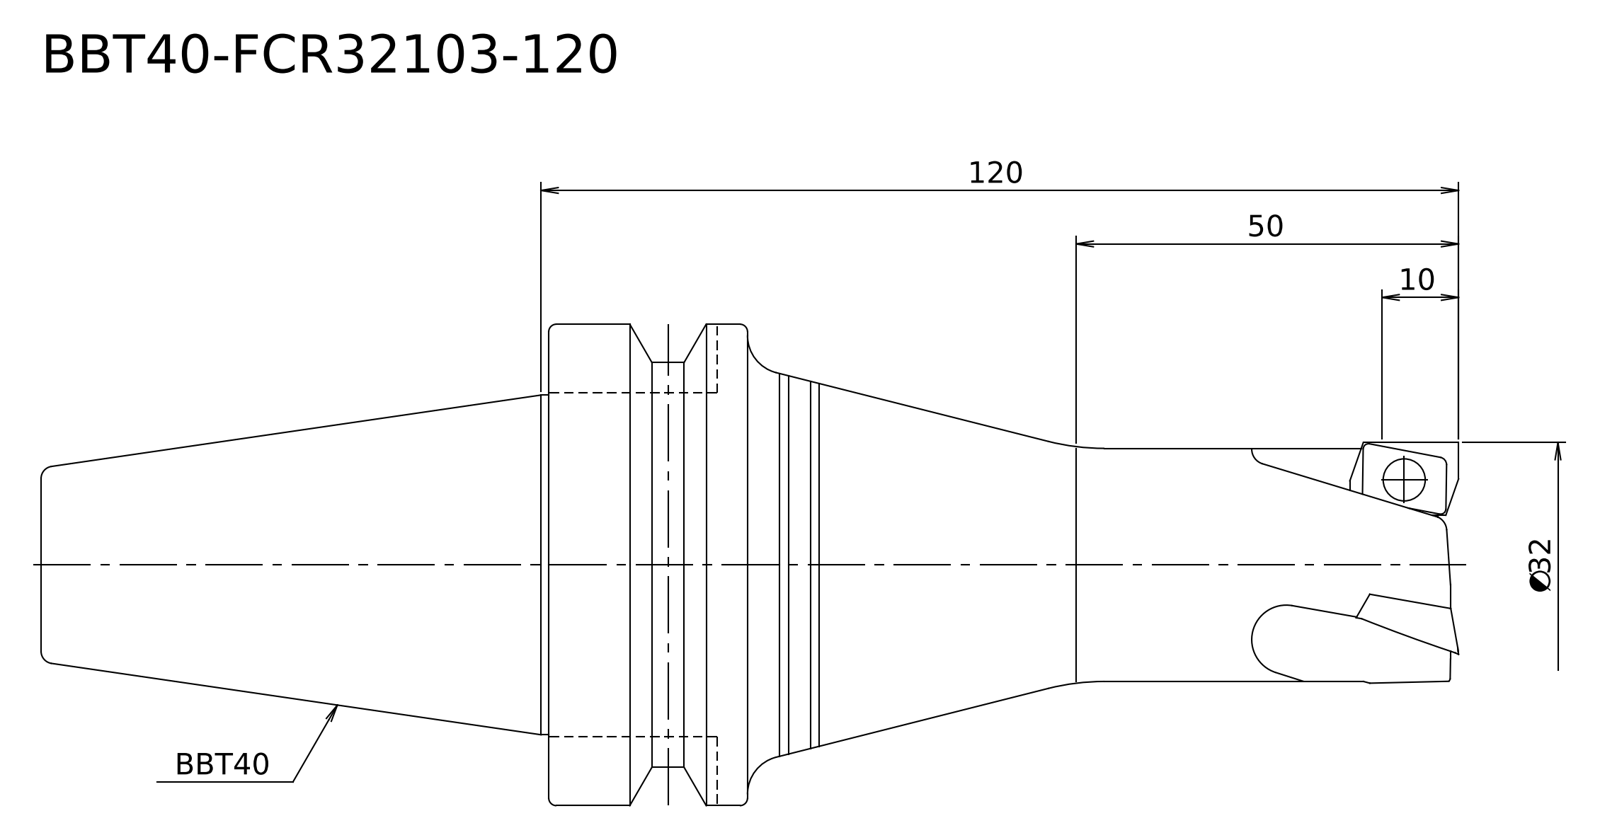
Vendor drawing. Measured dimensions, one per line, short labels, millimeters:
written by: Kubotek KeyCreator V8.5.1 (14335) (CONFIG_CONTROL_DESIGN)
unit: mm
bodies: 1 solid, 17 faces (4 planar, 6 cylindrical, 7 other)
size: 185.4 × 63 × 63
volume: 238 044 mm³; area: 27 586 mm²
bosses: 1× ⌀63, 1× ⌀53, 1× ⌀44.45, 1× ⌀32, 1× ⌀30.5
face distances: 119, 185.4, 66.4, 93, 26, 92.4
